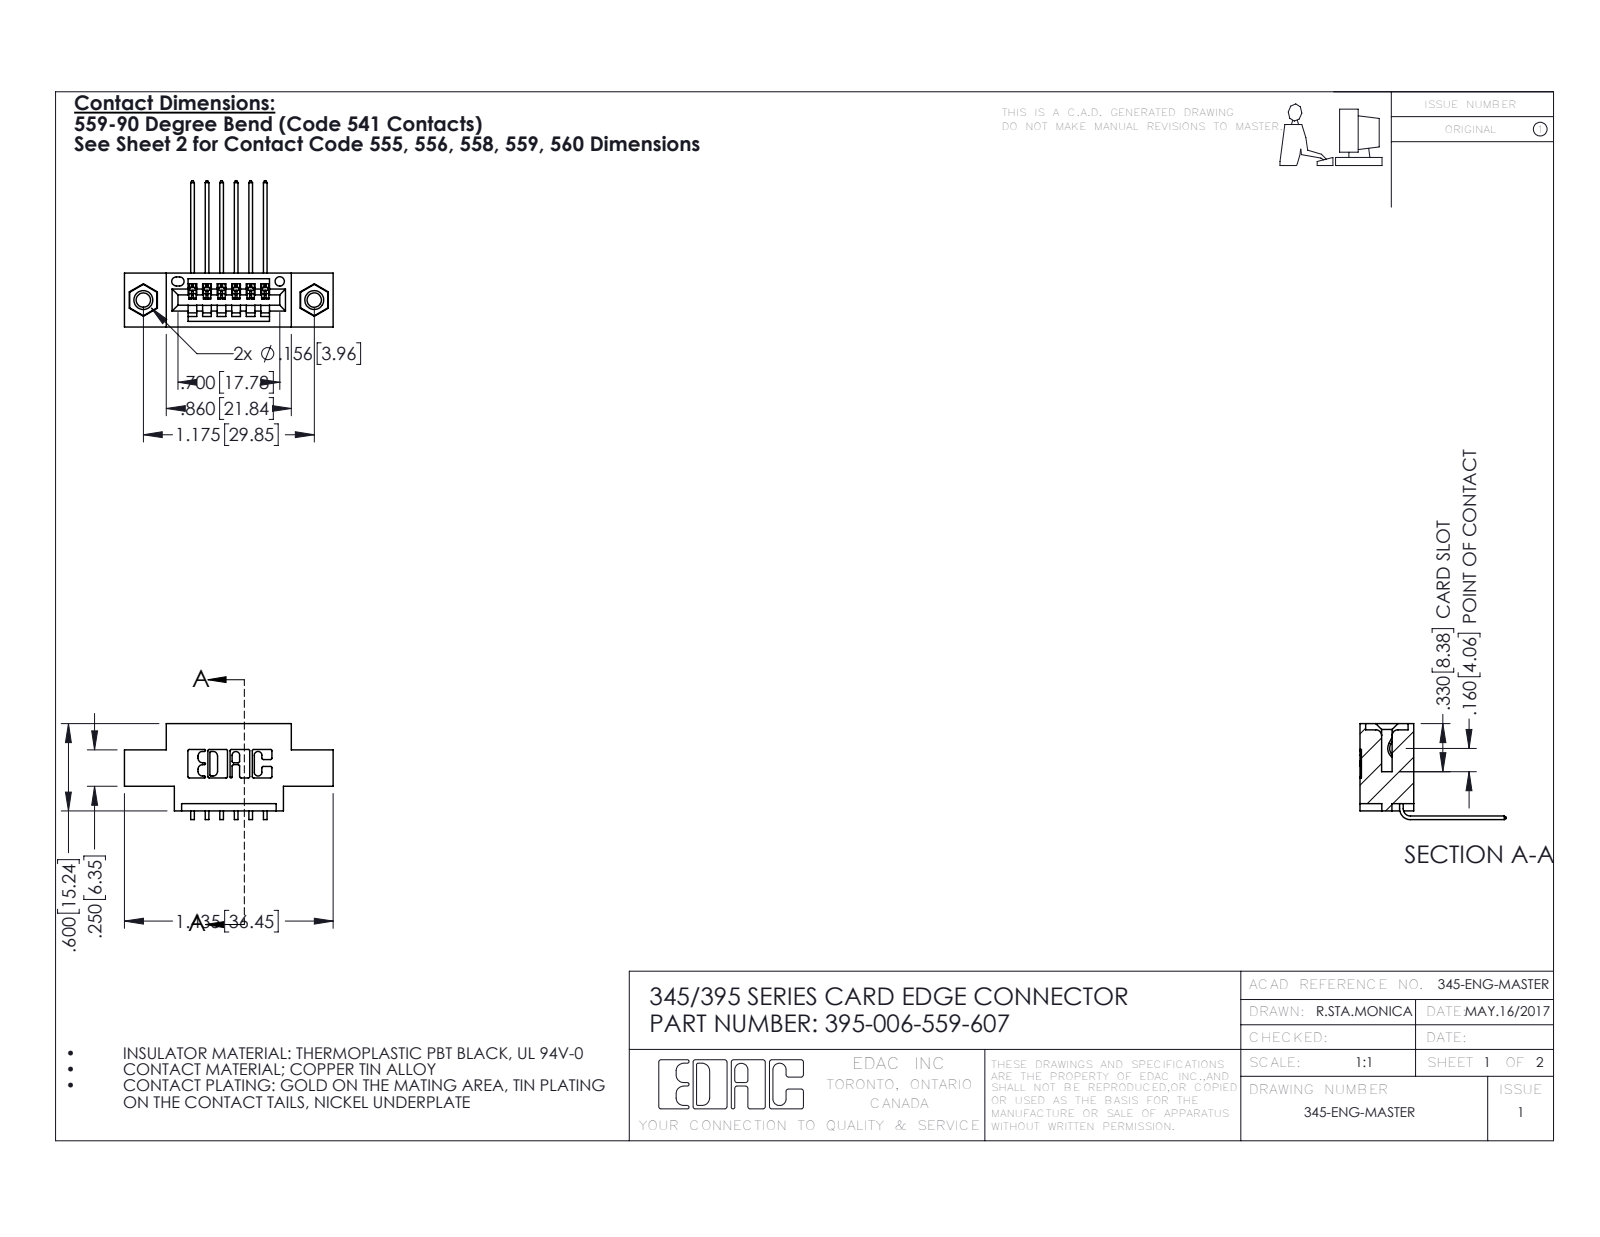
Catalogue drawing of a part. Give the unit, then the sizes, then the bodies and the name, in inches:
Units: inches
Overall size (bounding box): 1.435 × 1.005 × 0.659
Round holes (diameter × count): ⌀0.098 ×2, ⌀0.125 ×2, ⌀0.156 ×2, ⌀0.064 ×1
Round bosses / shafts (diameter × count): ⌀0.155 ×2
Partial cylindrical surfaces — rounded edges, fillets, slot ends (radius × count): R0.01 ×22, R0.006 ×12, R0.007 ×6, R0.031 ×6, R0.026 ×3, R0.031 ×2, R0.04 ×2, R0.014 ×1
Main face-to-face distances: 0.37, 0.2, 0.1, 0.072, 0.298, 0.025, 0.06, 0.3, 0.098, 0.272
Hole centre spacings: 0.27, 0.946, 1.175
Volume: 0.187 in³ · Surface area: 5.974 in²
Bodies: 9 solids, 550 faces (368 planar, 166 cylindrical, 16 other)
Part name (STEP PRODUCT): 345-250-001_345-250-005-103; 395-006-559-607; 345-292-001_558 559 Tail - 1; 345 Part_0.170 Offset - 0.156 Dia-TI
STEP written by: SolidWorks 2016 (CONFIG_CONTROL_DESIGN)
